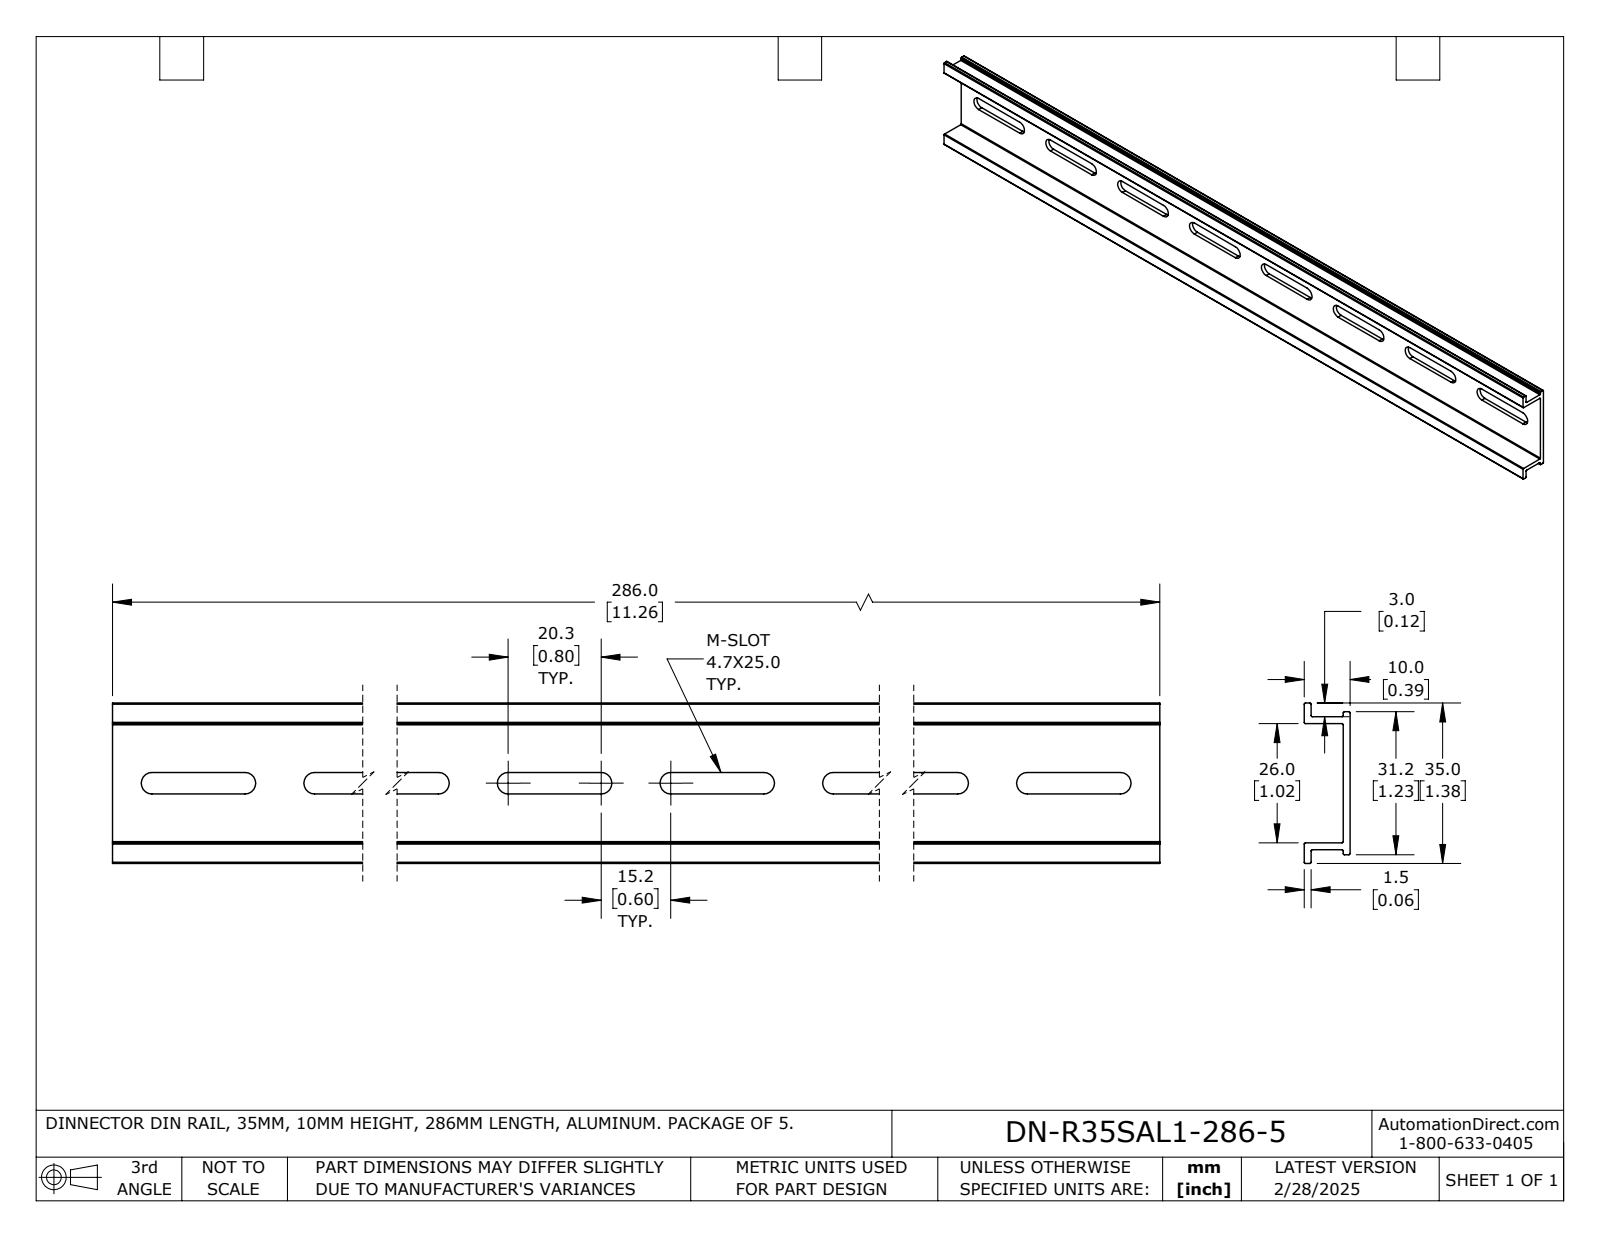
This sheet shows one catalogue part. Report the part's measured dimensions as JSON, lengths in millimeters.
{"part_name": "DN-R35SAL1-286-5_Default", "step_written_by": "SolidWorks 2024 (CONFIG_CONTROL_DESIGN)", "units": "millimeters", "bodies": {"solids": 1, "faces": 66, "planar": 34, "cylindrical": 32, "other": 0}, "overall_size": [286, 35, 10], "volume_mm3": 21881, "surface_area_mm2": 30357, "partial_cylinders_radius": [[0.27, 16], [2.35, 16]], "face_to_face_distances": [1.5, 27.5, 8.5, 26, 10, 29, 7, 1.1, 2.6, 28.6]}
